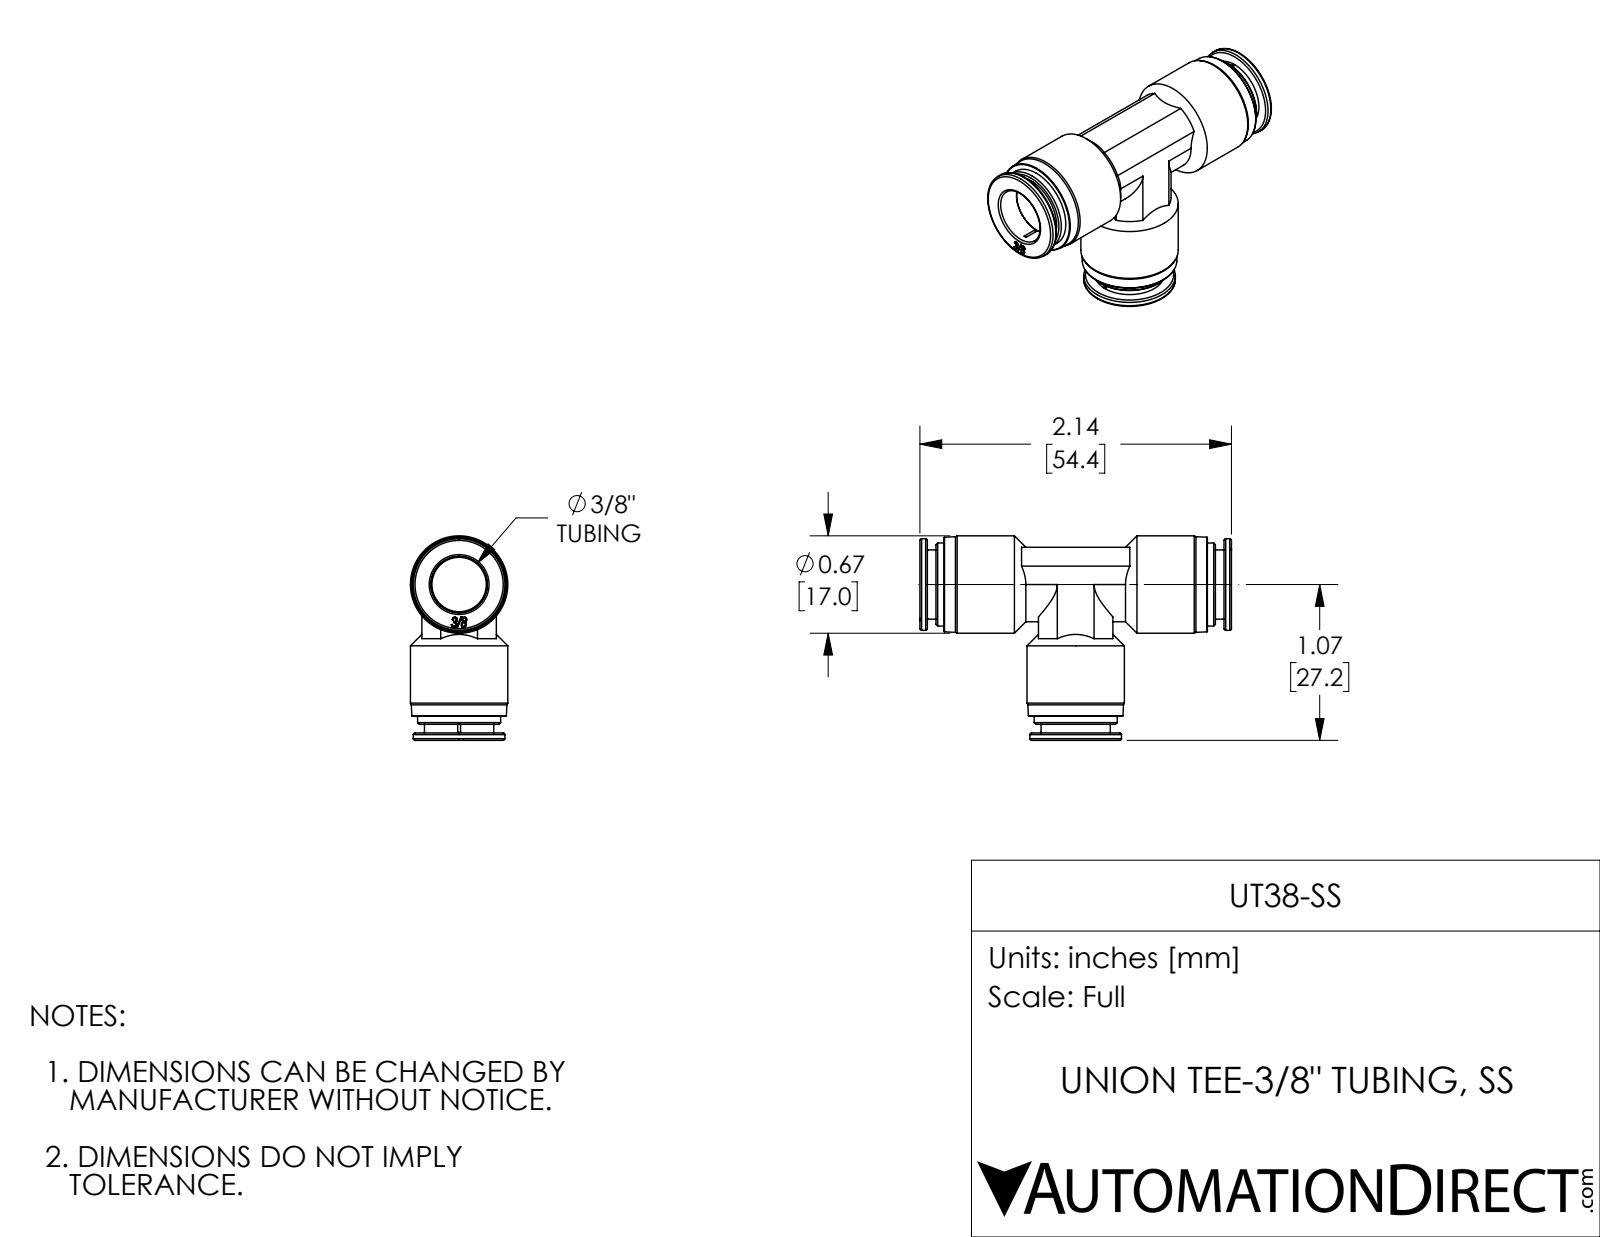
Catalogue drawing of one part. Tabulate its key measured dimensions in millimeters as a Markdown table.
| quantity | value |
| --- | --- |
| part name | UT38-SS |
| STEP written by | SolidWorks 2017 (AUTOMOTIVE_DESIGN) |
| units | millimeters |
| bodies | 1 solid, 282 faces (77 planar, 49 cylindrical, 156 other) |
| overall size | 54.4 × 35.7 × 17 |
| volume | 8 560 mm³ |
| surface area | 7 187 mm² |
| round holes (diameter × count) | 9.5 × 2, 9.75 × 2, 9.85 × 2 |
| round bosses / shafts (diameter × count) | 17 × 2, 16 × 2, 14.5 × 2, 12.1 × 2 |
| partial cylindrical surfaces (radius × count) | 6.5 × 1 |
| main face-to-face distances | 1.3, 4.2, 2.9, 53.1, 33.7, 13, 32.4, 50.2, 48.9, 54.4 |
